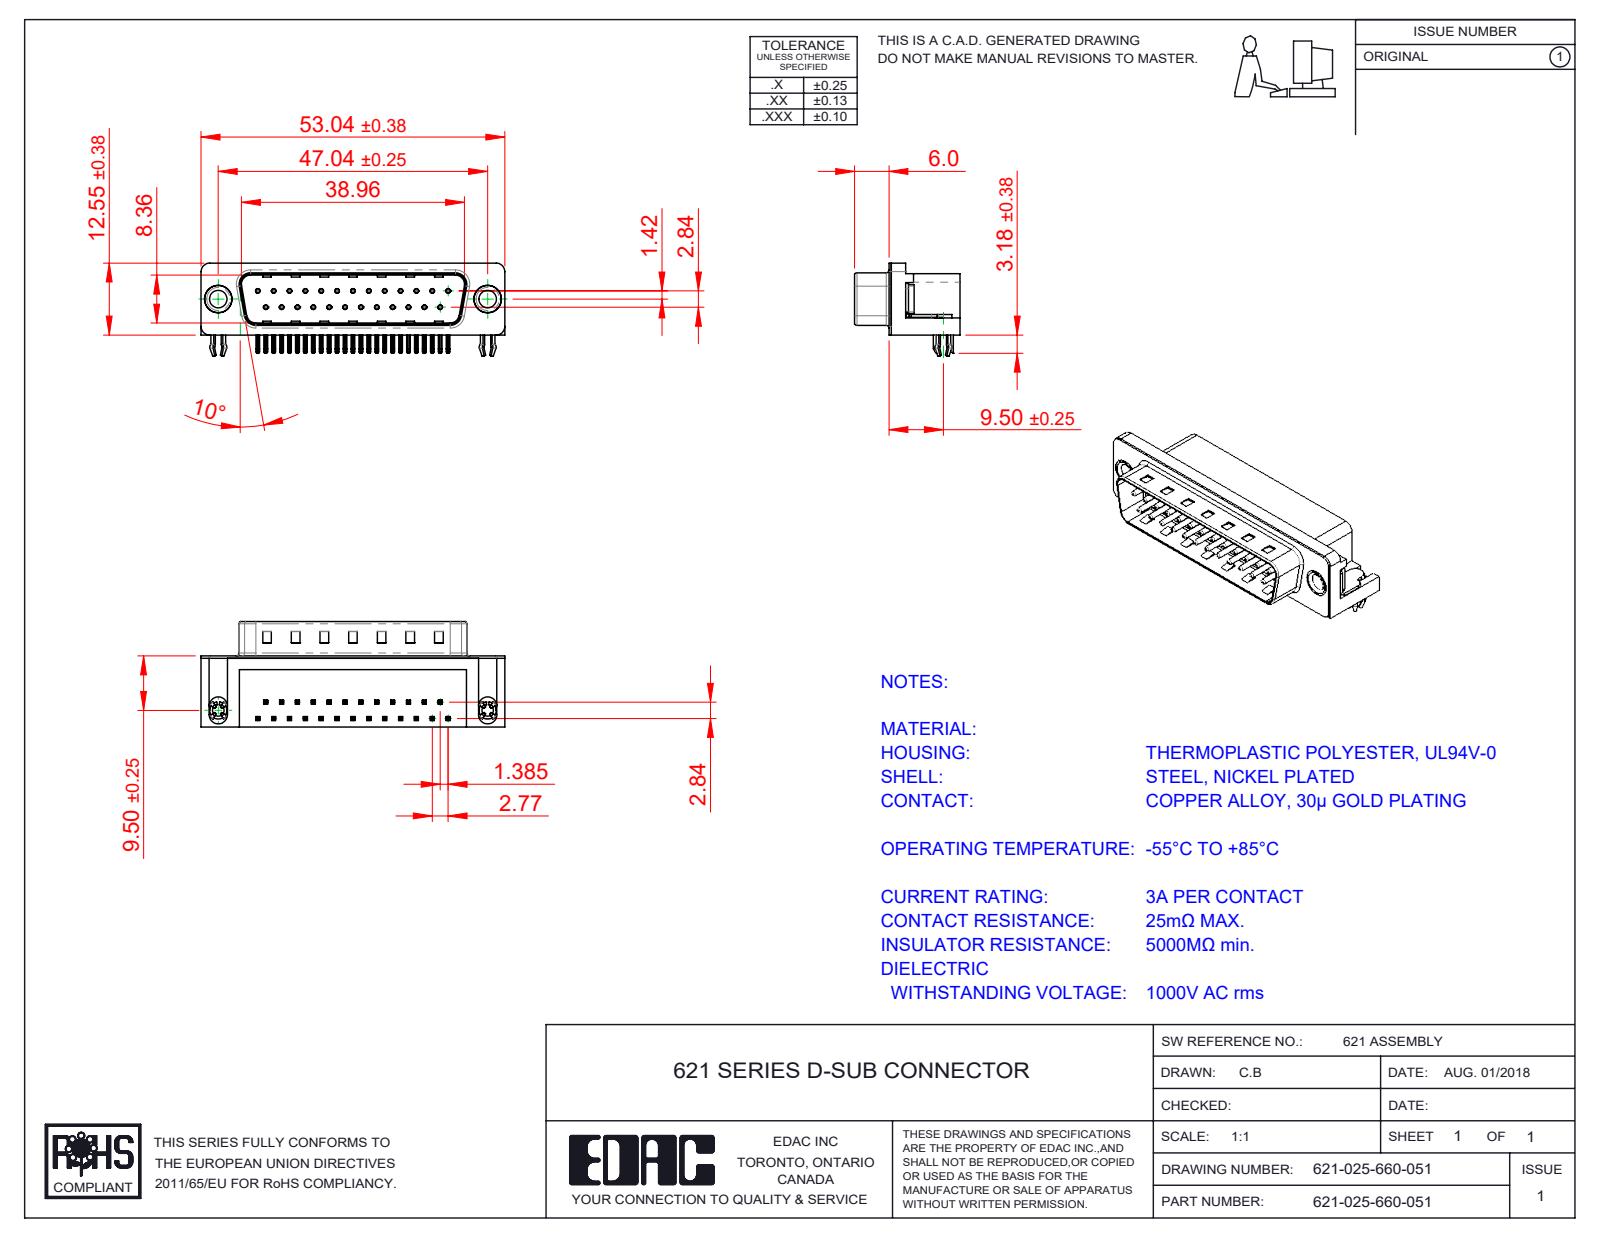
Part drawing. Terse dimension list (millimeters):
name: 621-025-660-051; 621 Thru Hole Rivet; 621 Shell_25 Socket; 621 Contact Top (+3 more)
written by: SolidWorks 2016 (CONFIG_CONTROL_DESIGN)
unit: mm
bodies: 31 solids, 2253 faces (1405 planar, 653 cylindrical, 195 other)
size: 53.04 × 18.4 × 15.73
volume: 6 347 mm³; area: 7 738 mm²
holes: 25× ⌀0.35, 25× ⌀0.8, 2× ⌀2.26, 2× ⌀3.05, 2× ⌀4, 2× ⌀4.8, 2× ⌀5
bosses: 25× ⌀0.75, 2× ⌀4.9, 2× ⌀4.75, 2× ⌀3.85, 2× ⌀3.26
rounds: 108× R0.25, 50× R0.12, 16× R1, 9× R0.5, 8× R1.6, 7× R1.5, 4× R0.9, 4× R2
face distances: 0.4, 12, 10.35, 2.1, 8.76, 10.46, 1.7, 10.86, 12.4, 9
hole spacings: 3.16, 2.77, 5.54, 8.31, 11.08, 13.85, 16.62, 5.03
